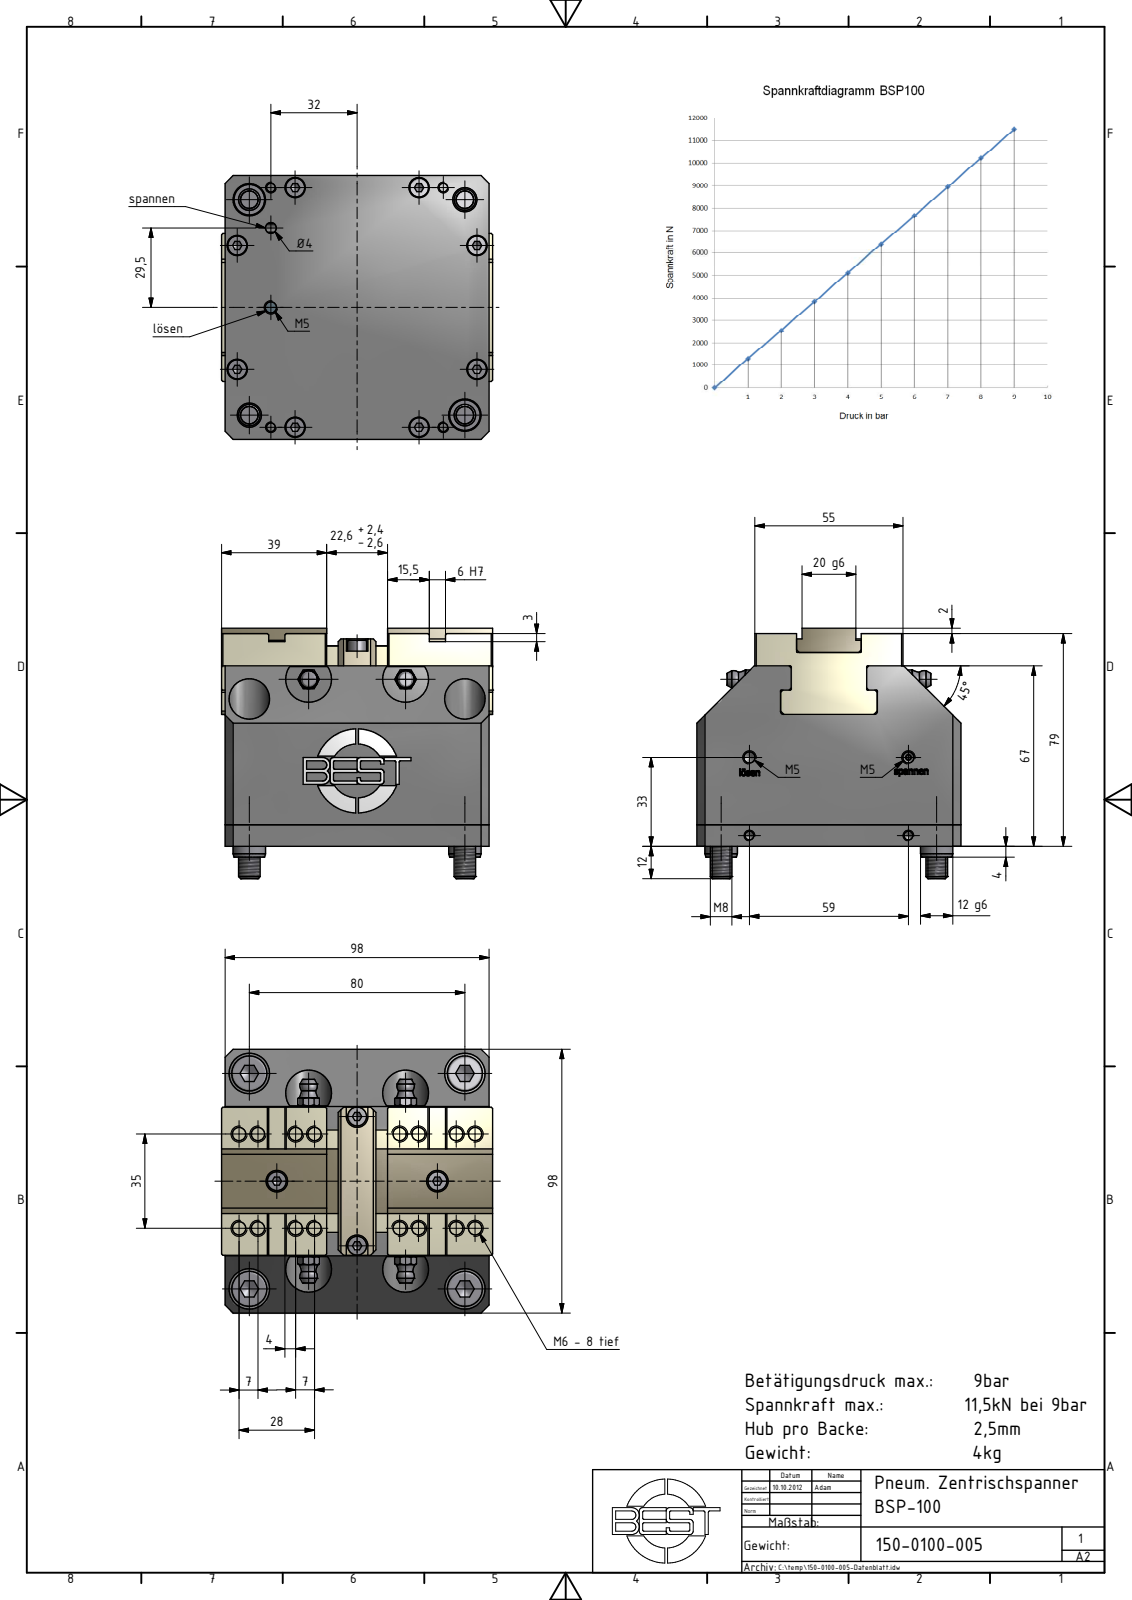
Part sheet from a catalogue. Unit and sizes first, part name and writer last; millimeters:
Units: millimetres
Overall size (bounding box): 100.6 × 98 × 93
Round holes (diameter × count): ⌀4.92 ×16, ⌀9 ×4, ⌀15 ×4, ⌀4.13 ×3, ⌀4 ×1
Round bosses / shafts (diameter × count): ⌀13 ×4, ⌀8 ×4, ⌀12 ×2
Partial cylindrical surfaces — rounded edges, fillets, slot ends (radius × count): R0.5 ×18, R1.25 ×12, R1.56 ×4, R2.81 ×4, R8.5 ×2, R10 ×1, R15.62 ×1
Main face-to-face distances: 98, 2, 31, 66.9, 1.3, 99.3, 76.5, 21.5, 46.5, 67
Hole centre spacings: 7, 21, 35, 35.69, 40.82, 59.6, 69.12, 14
Volume: 635 603 mm³ · Surface area: 71 742 mm²
Bodies: 1 solid, 558 faces (359 planar, 112 cylindrical, 87 other)
Part name (STEP PRODUCT): 150-0100-005-Kunde_Konturvereinfachung_1
STEP written by: Autodesk Inventor 2012 (AUTOMOTIVE_DESIGN)
